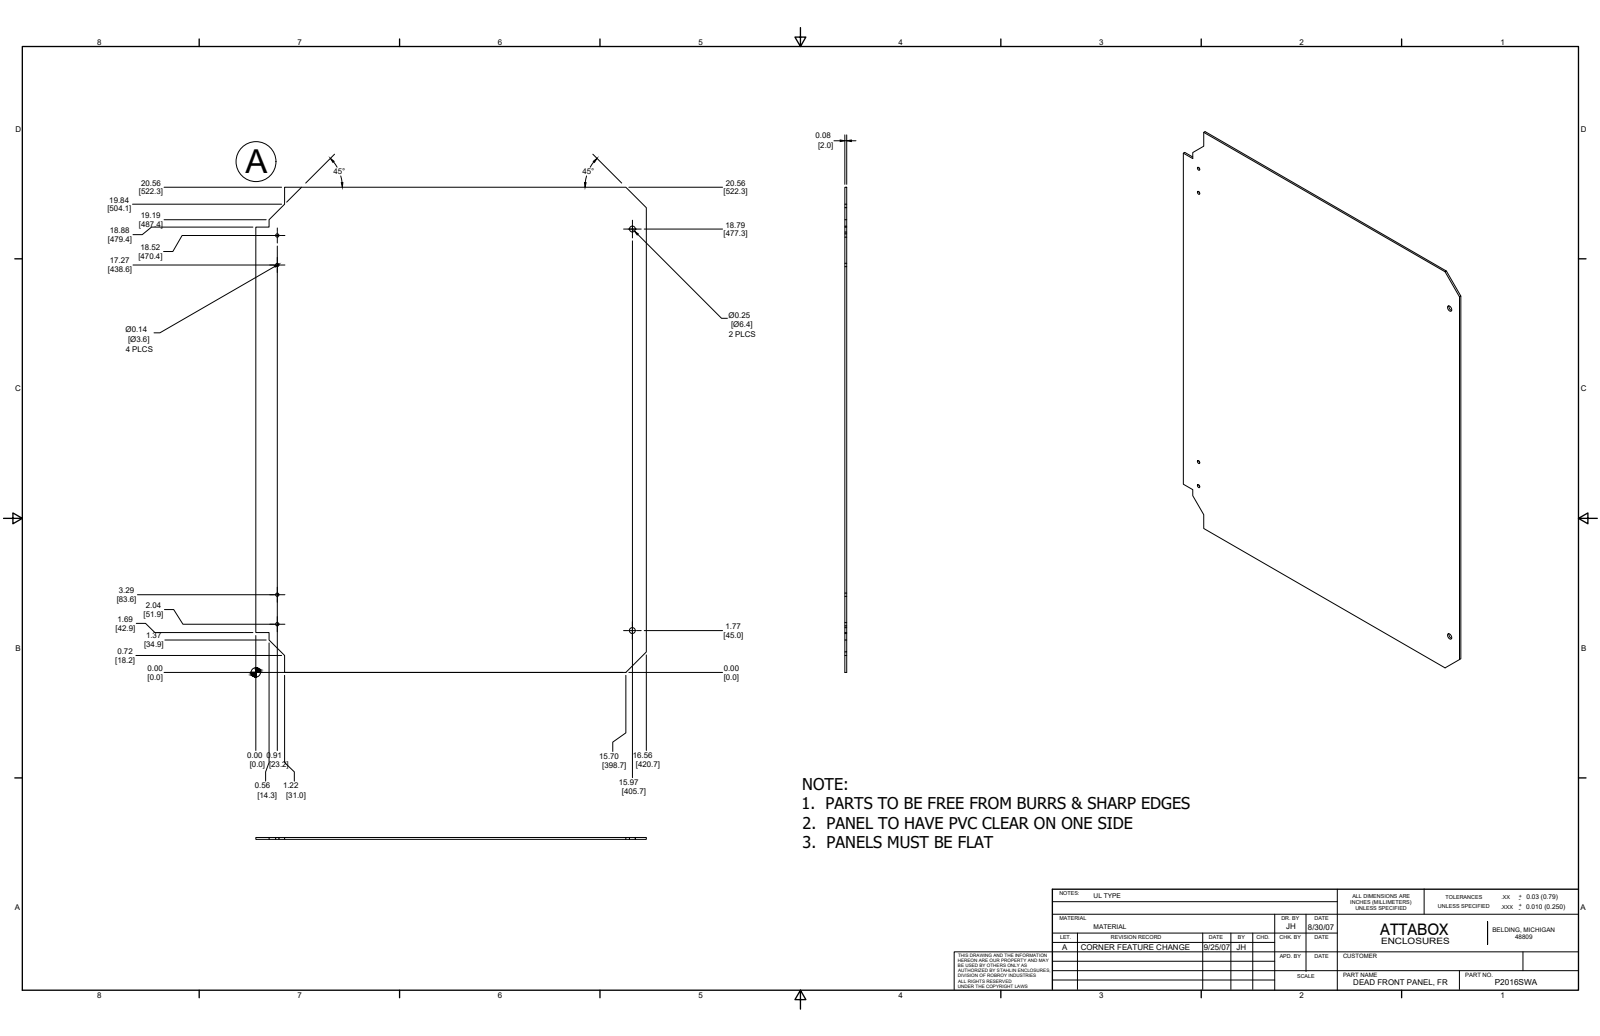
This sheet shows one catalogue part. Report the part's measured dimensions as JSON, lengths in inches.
{"part_name": "P2016SWAL", "step_written_by": "Autodesk Inventor 11 (AUTOMOTIVE_DESIGN)", "units": "inches", "bodies": {"solids": 1, "faces": 20, "planar": 14, "cylindrical": 6, "other": 0}, "overall_size": [20.563, 16.563, 0.08], "volume_in3": 27, "surface_area_in2": 681, "round_holes": [[0.14, 4], [0.25, 2]], "face_to_face_distances": [0.08, 16.562, 20.562, 1.09, 19.472, 15.472, 24.397, 18.383], "hole_center_spacings": [1.25, 15.062, 15.137, 15.226, 21.609, 22.522, 13.976, 16.476]}
